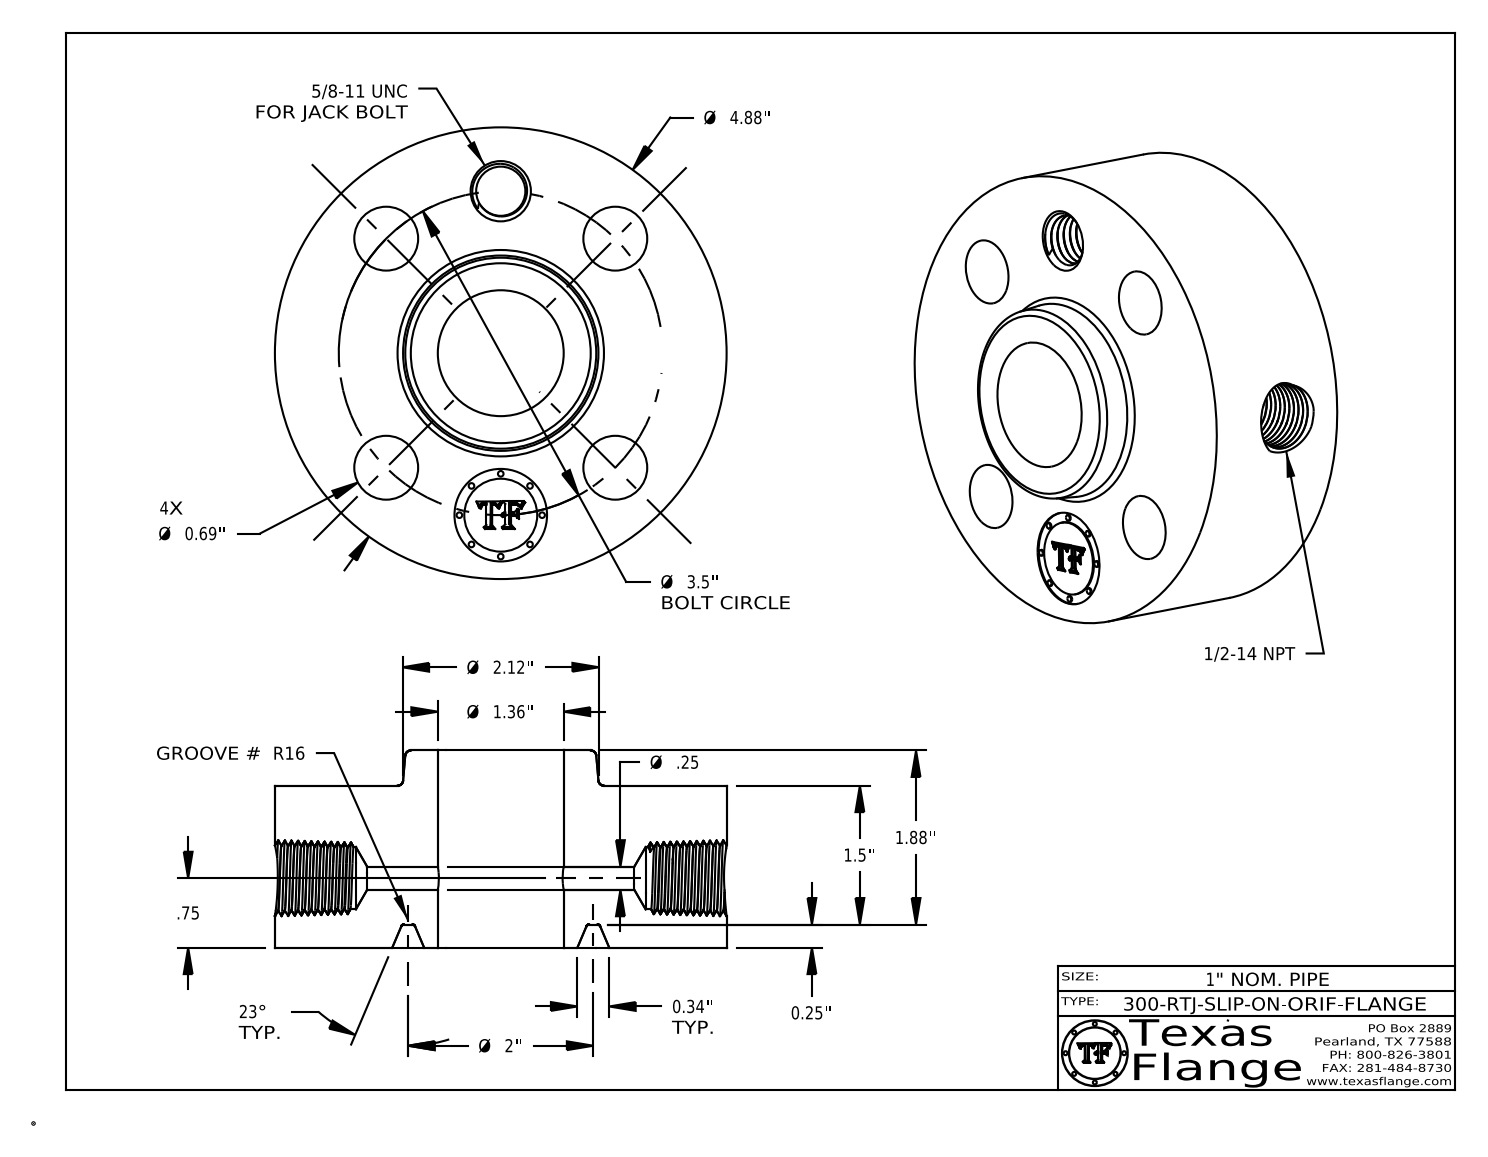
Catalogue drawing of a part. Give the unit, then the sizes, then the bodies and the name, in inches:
Units: inches
Overall size (bounding box): 4.88 × 4.88 × 2.13
Round holes (diameter × count): ⌀0.69 ×4, ⌀0.25 ×1, ⌀0.531 ×1, ⌀0.672 ×1, ⌀1 ×1, ⌀1.36 ×1
Round bosses / shafts (diameter × count): ⌀0.061 ×8, ⌀4.88 ×1, ⌀0.788 ×1
Main face-to-face distances: 1.75, 2.13, 0.38, 0.25, 1.5, 1.88, 1.735, 1.485, 0.015, 0.395
Hole centre spacings: 1.75, 1.339, 2.475, 3.233, 3.5
Volume: 26.63 in³ · Surface area: 98.82 in²
Bodies: 1 solid, 787 faces (370 planar, 89 cylindrical, 328 other)
Part name (STEP PRODUCT): 300-RTJ-SLIP-ON
STEP written by: CATIA V5 STEP AP214 (AUTOMOTIVE_DESIGN)
